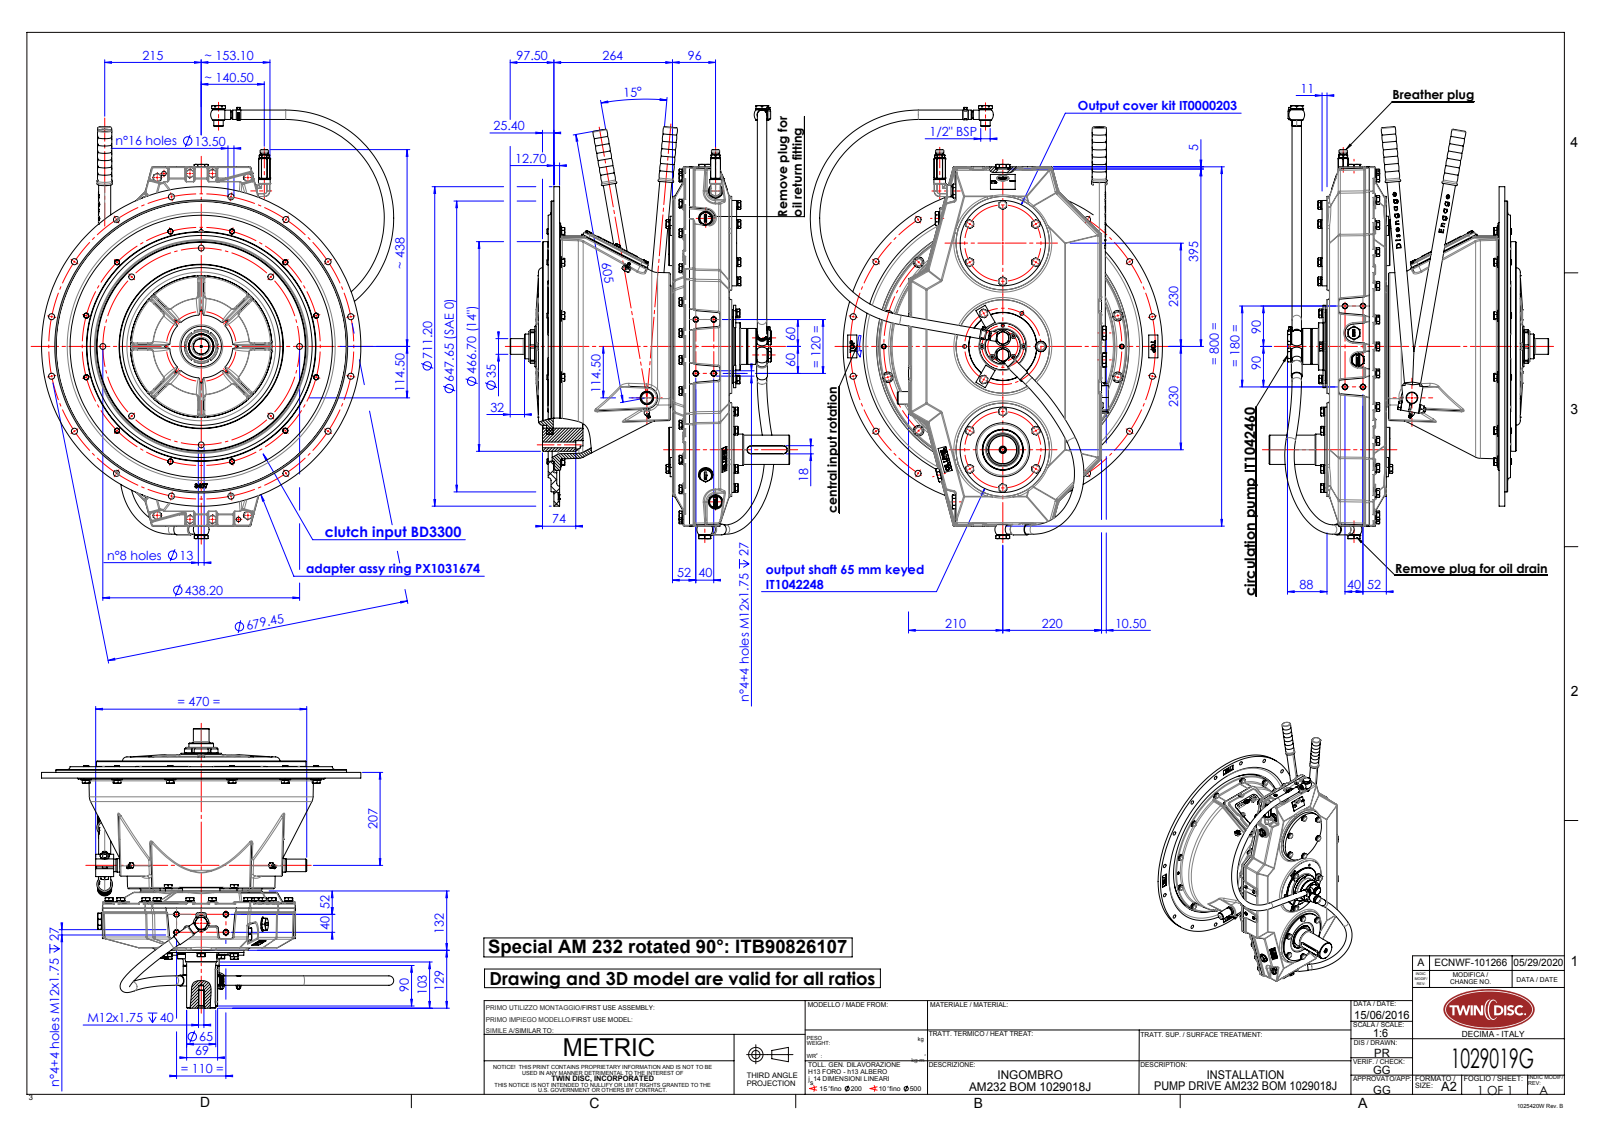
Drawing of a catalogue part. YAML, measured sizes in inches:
part_name: "1029019G; ITB90810000_rev00-installation; IT2021216_rev03-installation; IT1042248_rev01-installation (+7 more)"
step_written_by: "SolidWorks 2007 (AUTOMOTIVE_DESIGN)"
units: inches
bodies: {solids: 73, faces: 12907, planar: 5563, cylindrical: 3622, other: 3722}
overall_size: [37.962, 30.88, 24.528]
volume: 391.3
surface_area: 8024
round_holes:
  - {diameter: 0.402, count: 64}
  - {diameter: 0.413, count: 37}
  - {diameter: 0.335, count: 32}
  - {diameter: 0.472, count: 32}
  - {diameter: 0.512, count: 23}
  - {diameter: 0.433, count: 17}
  - {diameter: 0.531, count: 16}
  - {diameter: 0.276, count: 13}
  - {diameter: 0.394, count: 12}
  - {diameter: 0.437, count: 12}
  - {diameter: 0.469, count: 12}
  - {diameter: 0.827, count: 11}
round_bosses_or_shafts:
  - {diameter: 0.394, count: 54}
  - {diameter: 0.713, count: 45}
  - {diameter: 0.638, count: 45}
  - {diameter: 0.236, count: 13}
  - {diameter: 0.922, count: 12}
  - {diameter: 0.619, count: 12}
  - {diameter: 0.434, count: 12}
  - {diameter: 0.709, count: 10}
partial_cylinders:
  - {radius: 0.079, count: 286}
  - {radius: 0.118, count: 128}
  - {radius: 0.197, count: 124}
  - {radius: 0.098, count: 80}
  - {radius: 0.014, count: 58}
  - {radius: 1.163, count: 58}
  - {radius: 0.315, count: 35}
  - {radius: 0.02, count: 24}
face_to_face_distances: [0.5, 0.25, 0.669, 0.75, 0.591, 1, 0.079, 10.394, 10.472, 11.063]
hole_center_spacings: [10.437, 24.714, 5.219, 20.164, 22.242, 26.236, 3.474, 3.741]
